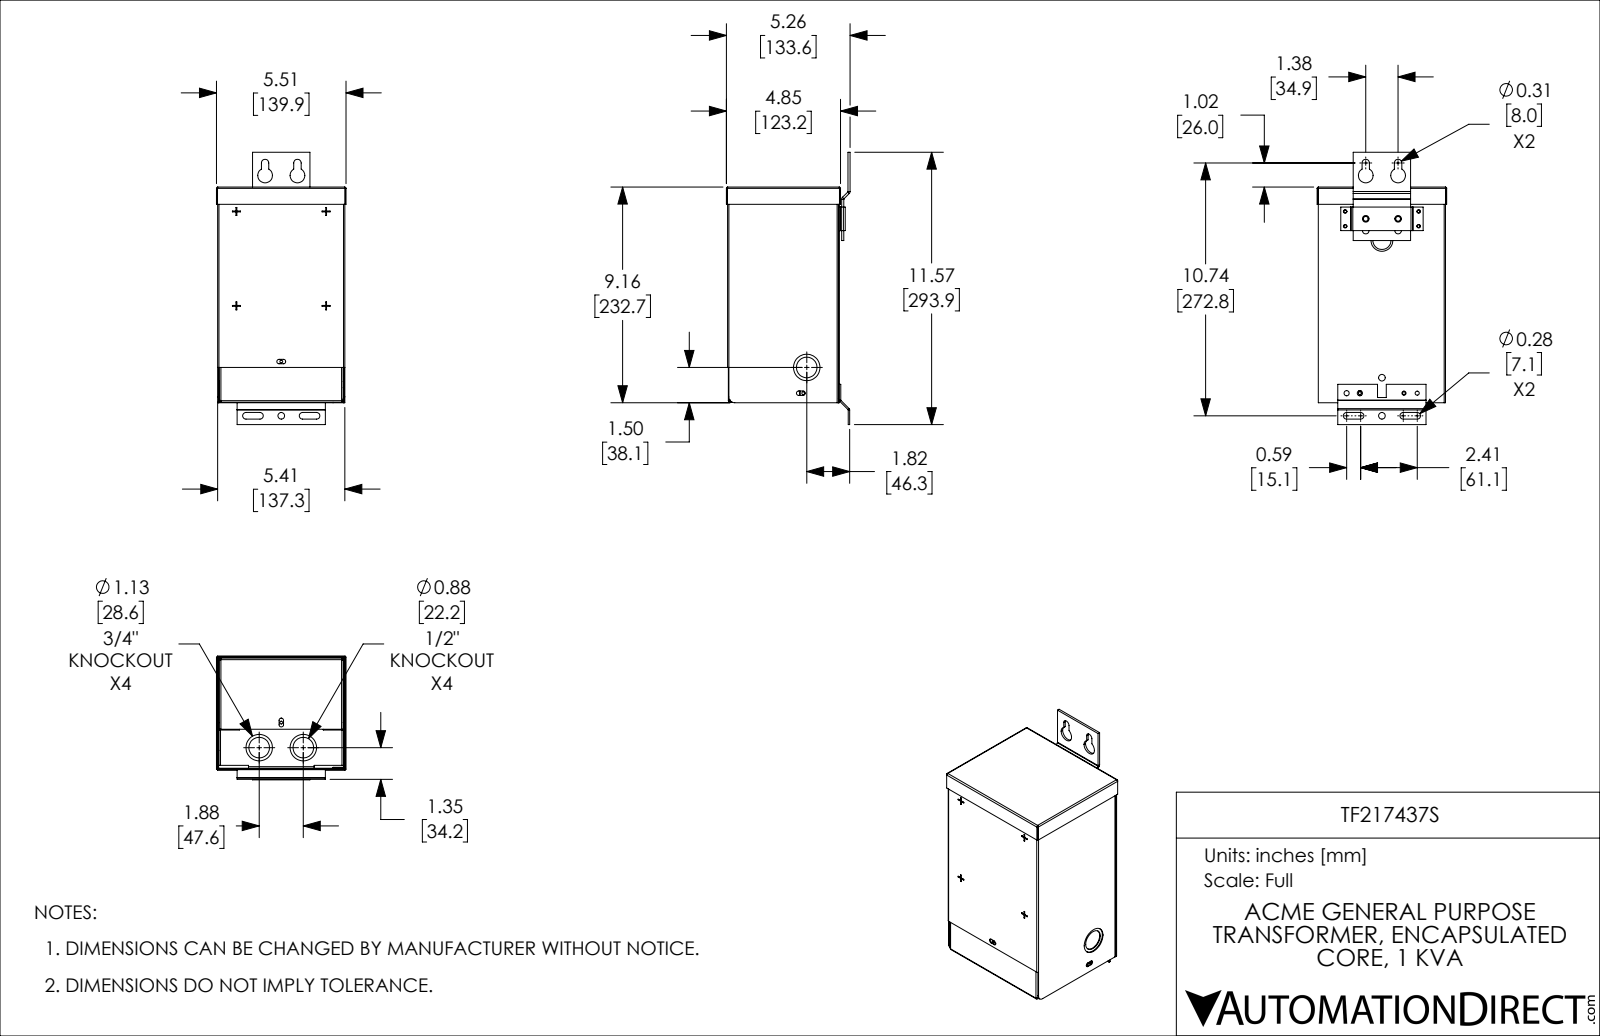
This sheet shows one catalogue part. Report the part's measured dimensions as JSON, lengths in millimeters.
{"part_name": "TF217437S", "step_written_by": "SolidWorks 2021 (CONFIG_CONTROL_DESIGN)", "units": "millimeters", "bodies": {"solids": 7, "faces": 521, "planar": 329, "cylindrical": 152, "other": 40}, "overall_size": [293.87, 139.9, 133.57], "volume_mm3": 177414, "surface_area_mm2": 368059, "round_holes": [[7.14, 6], [3.05, 5], [22.22, 3], [28.57, 3], [4.37, 2], [4.76, 2], [5.11, 2], [5.56, 2], [15.88, 2]], "round_bosses_or_shafts": [[29.79, 1], [23.44, 1]], "partial_cylinders_radius": [[0.51, 10], [2.38, 10], [0.79, 8], [1.42, 8], [1.7, 8], [0.38, 4], [1.9, 4], [3.57, 4]], "face_to_face_distances": [0.91, 119.74, 136.41, 118.83, 135.5, 137.32, 120.65, 231.14, 1.29, 2.2], "hole_center_spacings": [34.92, 12.7, 14.29, 29.09, 34.08, 35.98, 37.16, 41.6]}
